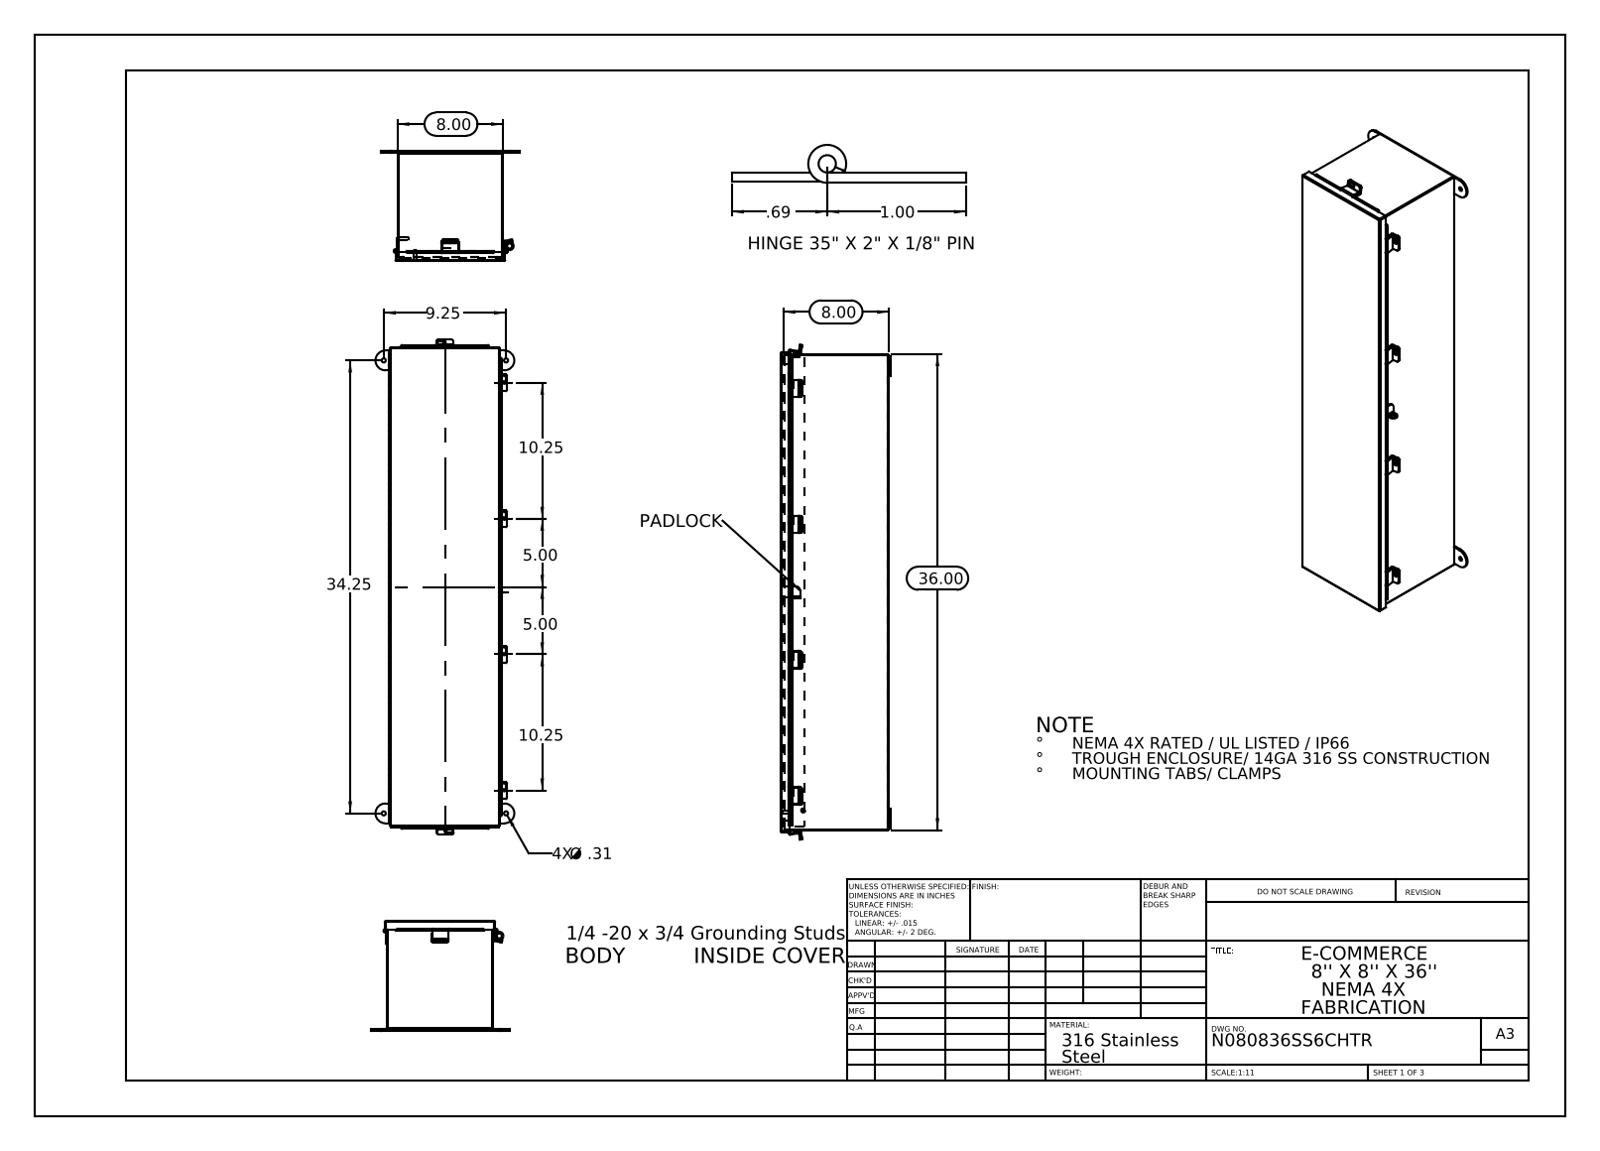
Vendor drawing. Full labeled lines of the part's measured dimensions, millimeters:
Part name (STEP PRODUCT): HW-CLH-JH-20154; N080836SSCHTR JIC_Cover_Template; N080836SSCHTR JIC Mounting Bracket; N080836SSCHTR JIC Top (+8 more)
STEP written by: SolidWorks 2013 (CONFIG_CONTROL_DESIGN)
Units: millimetres
Bodies: 23 solids, 1160 faces (705 planar, 435 cylindrical, 20 other)
Overall size (bounding box): 950.1 × 266.7 × 211.8
Volume: 1 845 000 mm³ · Surface area: 1 949 000 mm²
Round holes (diameter × count): ⌀6.4 ×6, ⌀8 ×4, ⌀3.2 ×1, ⌀9.5 ×1
Round bosses / shafts (diameter × count): ⌀8 ×2, ⌀6 ×2, ⌀6.9 ×1, ⌀6.4 ×1
Partial cylindrical surfaces — rounded edges, fillets, slot ends (radius × count): R3.2 ×23, R0.2 ×12, R3.4 ×12, R0.3 ×10, R2.2 ×10, R2.1 ×6, R2.5 ×6, R19.1 ×4
Main face-to-face distances: 1.9, 201.3, 206.5, 203.2, 199.4, 208.4, 204.5, 912.5, 3.8, 205.1
Hole centre spacings: 235, 261.3, 522.3, 870, 901.1, 219.3, 261, 783.6
